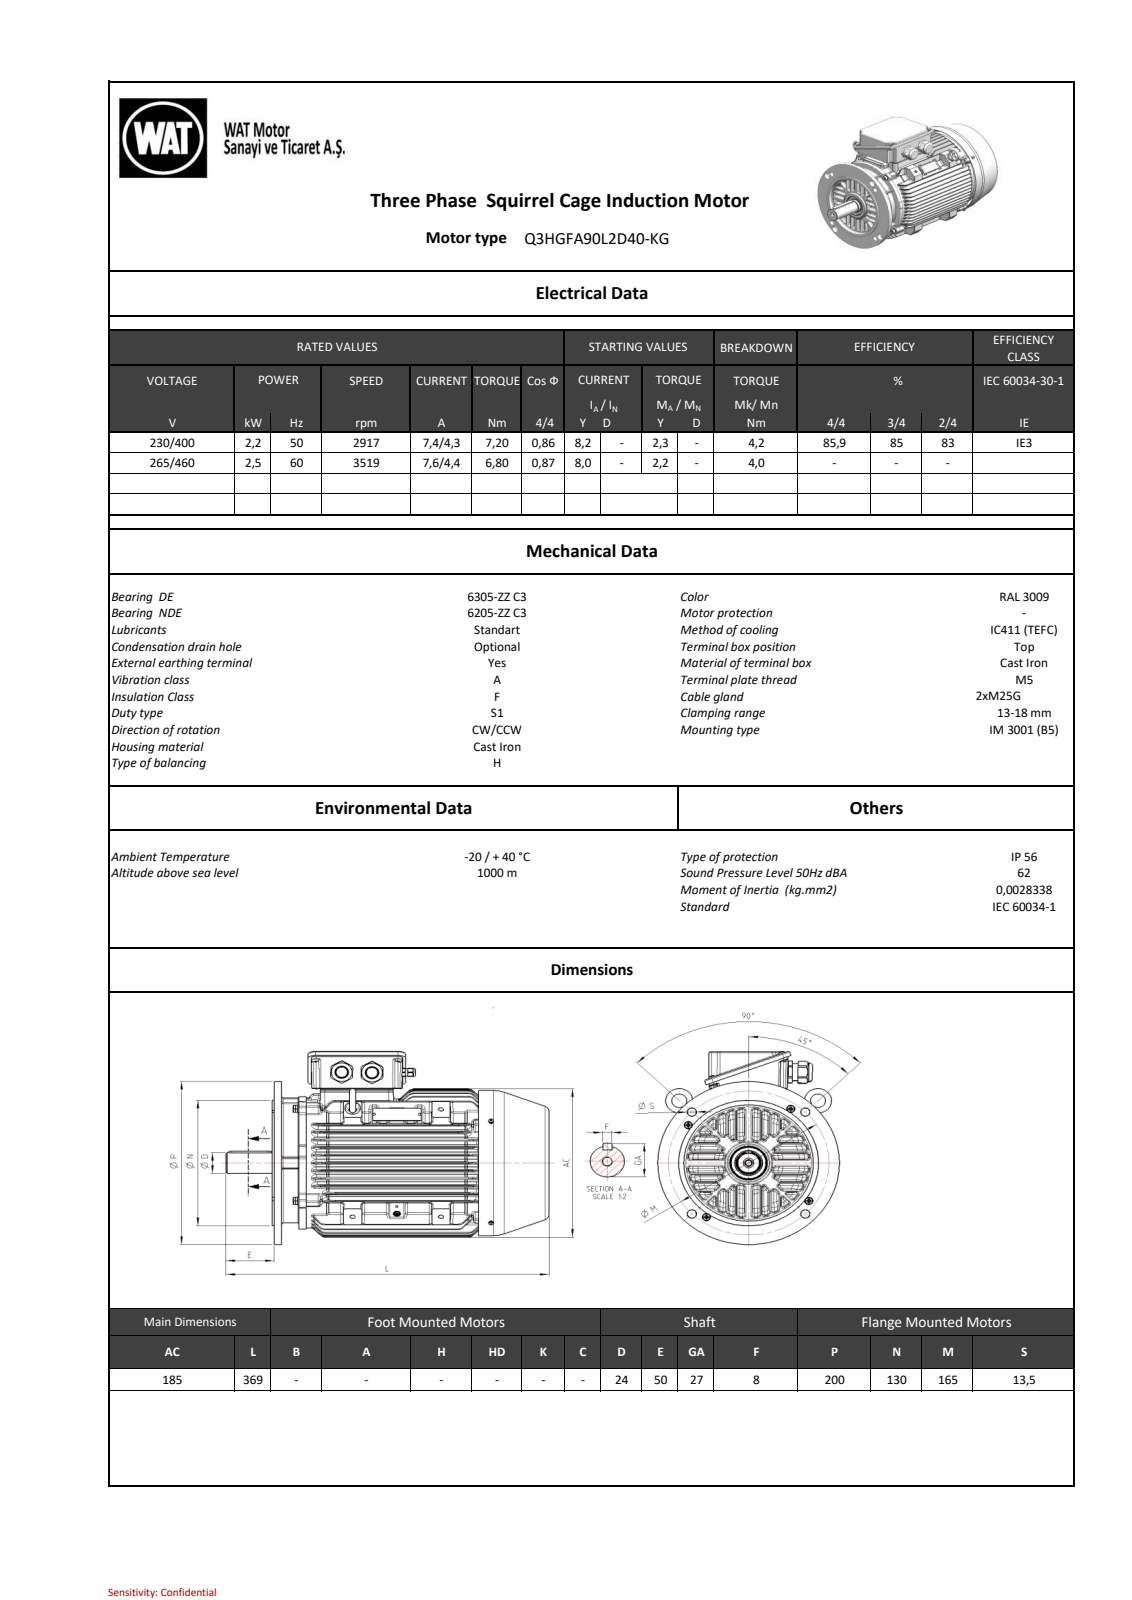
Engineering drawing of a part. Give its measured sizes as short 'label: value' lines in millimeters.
name: C901A24426BAzcva
written by: SIEMENS PLM Software NX 11.0 (AUTOMOTIVE_DESIGN)
unit: mm
bodies: 0 solids, 2989 faces (836 planar, 844 cylindrical, 1309 other)
size: 368.47 × 241.98 × 226.53
holes: 6× ⌀10, 4× ⌀13.5, 2× ⌀2.5, 2× ⌀17.2, 1× ⌀6.5, 1× ⌀6.8, 1× ⌀8.4, 1× ⌀36.9, 1× ⌀37.1, 1× ⌀174
bosses: 4× ⌀20, 3× ⌀8.65, 3× ⌀8, 3× ⌀5, 2× ⌀27.7, 2× ⌀25.25, 1× ⌀200, 1× ⌀176
rounds: 316× R1.5, 39× R2, 38× R4, 28× R3, 24× R1, 18× R1.2, 12× R5, 12× R26.5
face distances: 12.04, 6.5, 262.18, 268.68, 49.79, 311.97, 318.47, 62.58, 3.01, 1.5
hole spacings: 116.67, 80.5, 139.43, 21.36, 82.5, 99.24, 129.32, 150.59
